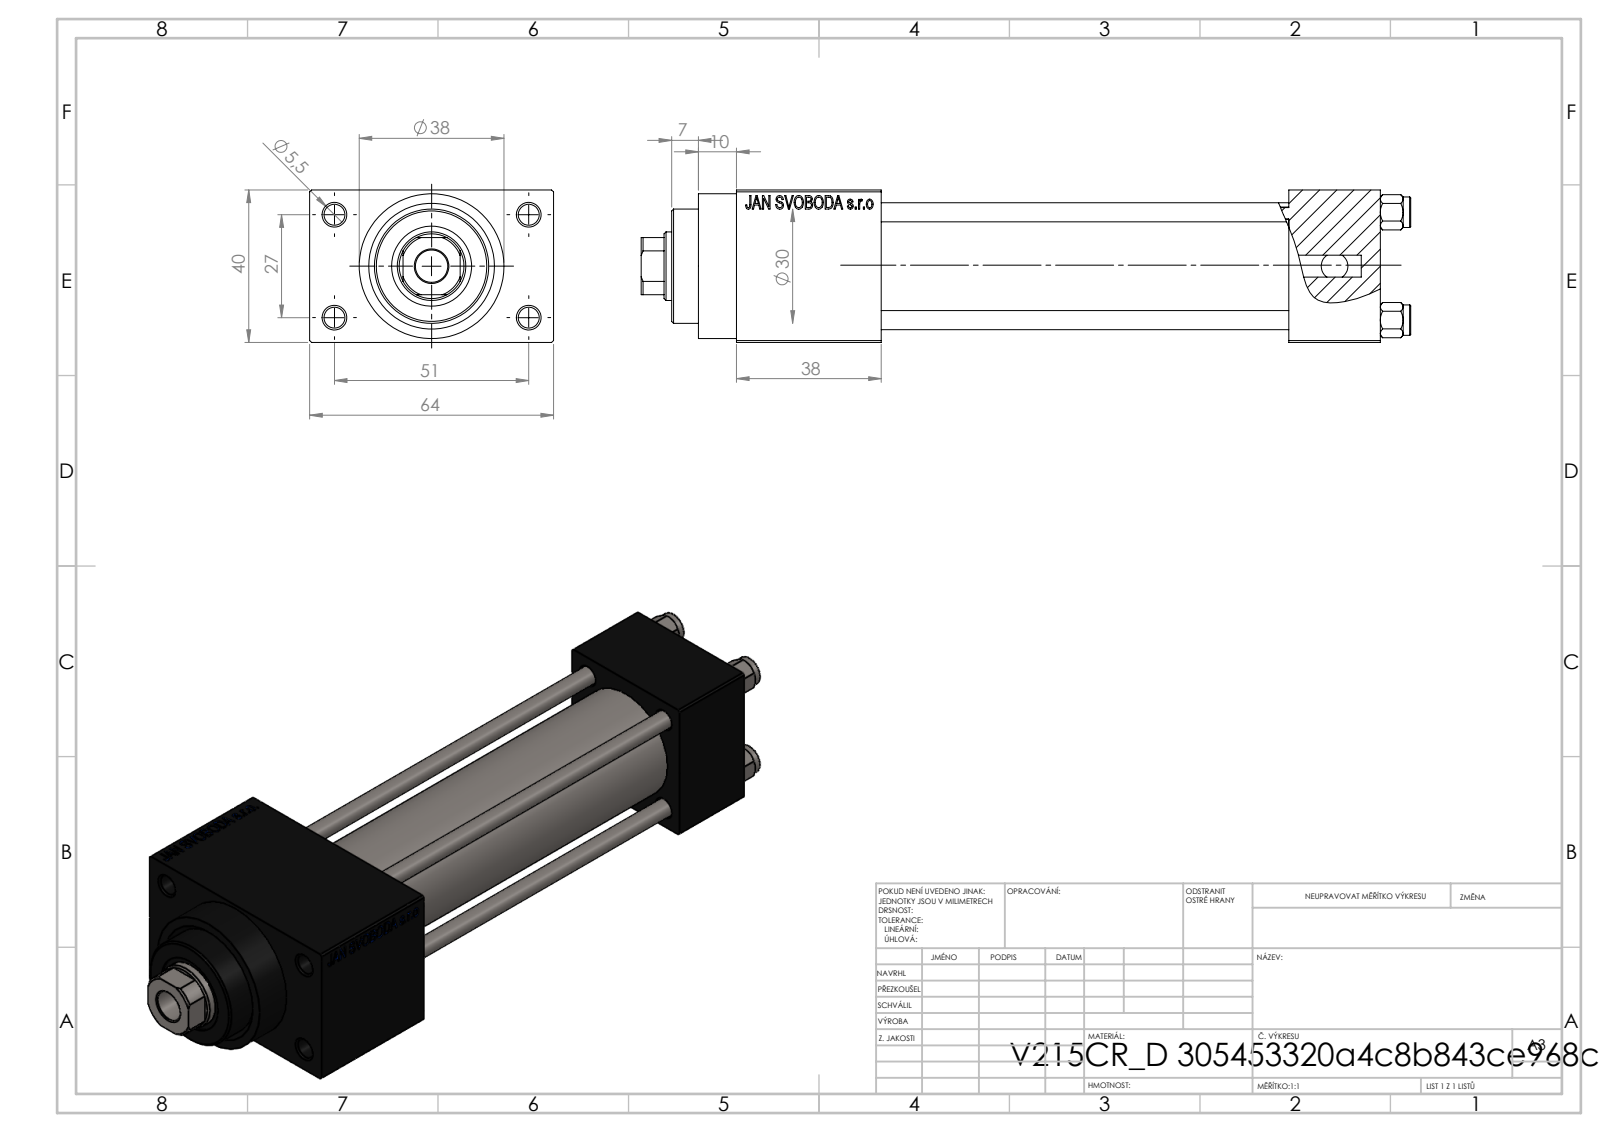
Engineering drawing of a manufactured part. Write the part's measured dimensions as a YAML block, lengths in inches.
part_name: "V215_VC_A; V215CR_VCP_D; V215CR_D_Body; V215CR_D_TYCINKA (+1 more)"
step_written_by: "SolidWorks 2019 (CONFIG_CONTROL_DESIGN)"
units: inches
bodies: {solids: 11, faces: 1101, planar: 495, cylindrical: 86, other: 520}
overall_size: [7.953, 2.52, 1.575]
volume: 13.12
surface_area: 127.6
round_holes:
  - {diameter: 0.197, count: 4}
  - {diameter: 0.217, count: 4}
  - {diameter: 0.787, count: 3}
  - {diameter: 0.276, count: 2}
  - {diameter: 0.518, count: 2}
  - {diameter: 0.335, count: 1}
  - {diameter: 0.709, count: 1}
  - {diameter: 0.827, count: 1}
  - {diameter: 0.984, count: 1}
  - {diameter: 1.181, count: 1}
round_bosses_or_shafts:
  - {diameter: 0.315, count: 4}
  - {diameter: 1.496, count: 1}
  - {diameter: 1.22, count: 1}
partial_cylinders:
  - {radius: 0.335, count: 1}
face_to_face_distances: [1.575, 0.472, 4.213, 0.945, 5.157, 2.047, 1.496, 6.654, 5.709, 2.52]
hole_center_spacings: [0.448, 0.788, 1.114, 1.136, 1.177, 1.561, 1.903, 1.063]
